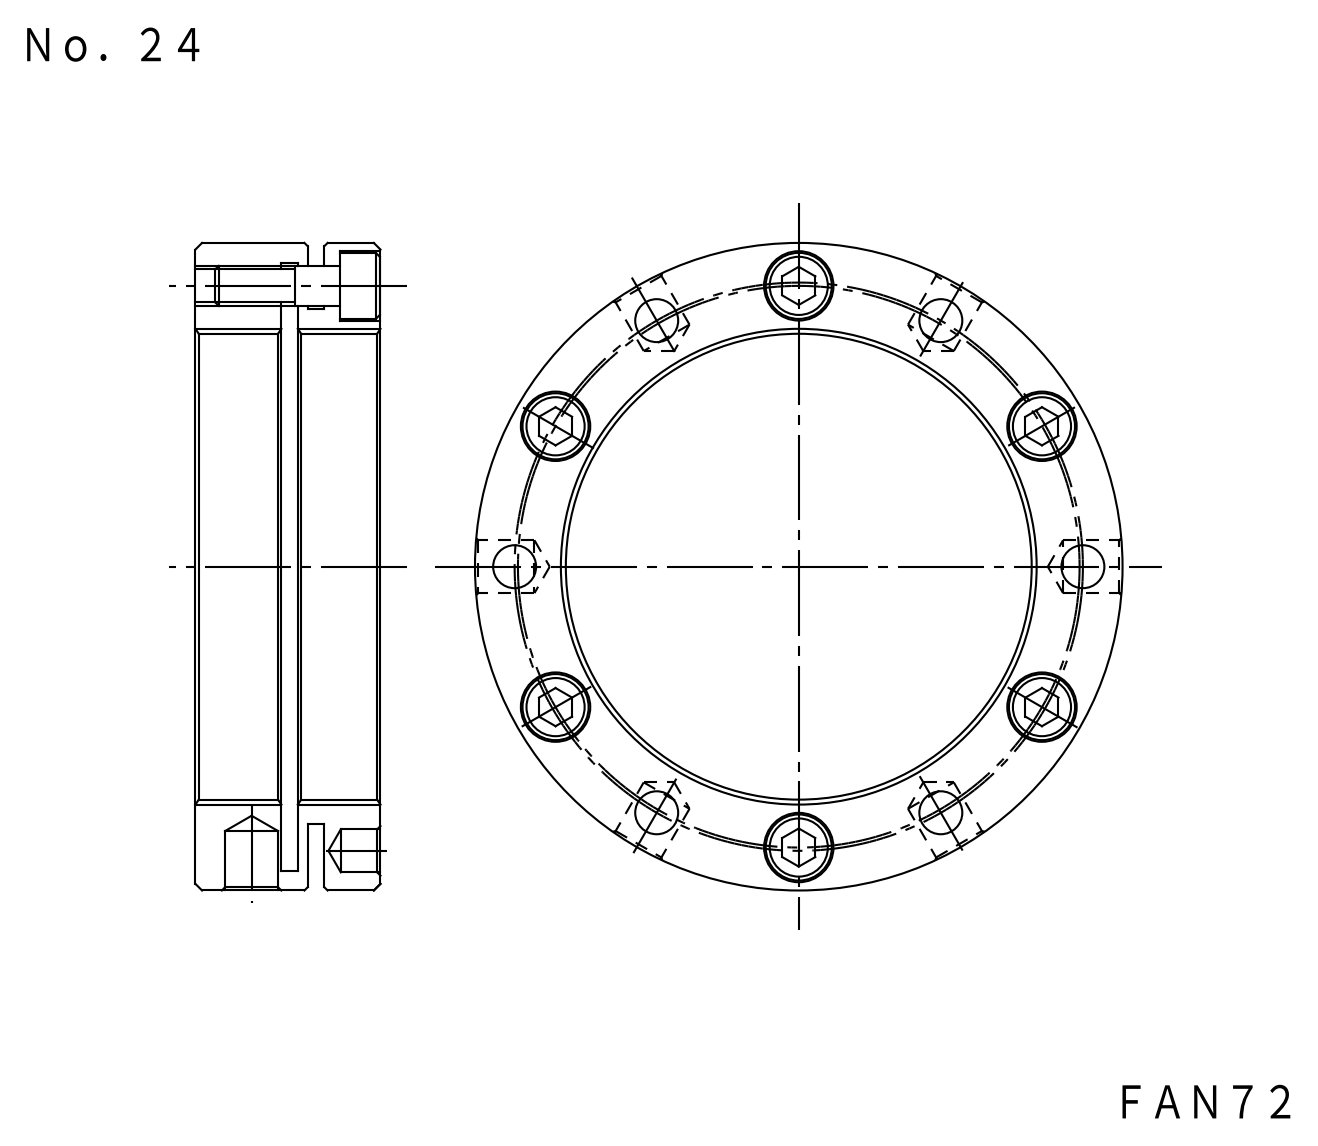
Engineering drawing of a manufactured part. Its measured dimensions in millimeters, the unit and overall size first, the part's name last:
Units: millimetres
Overall size (bounding box): 98 × 98 × 28
Round holes (diameter × count): ⌀6.3 ×6, ⌀6.5 ×6, ⌀10.5 ×6, ⌀4.92 ×3, ⌀4.92 ×3, ⌀8 ×3, ⌀72 ×1, ⌀92 ×1
Round bosses / shafts (diameter × count): ⌀10 ×6, ⌀6 ×6, ⌀98 ×1, ⌀78 ×1
Main face-to-face distances: 2.5, 4, 28, 20, 8, 17.5, 10.5, 13.5, 6.5, 14.5
Hole centre spacings: 42.5, 43, 60.46, 82.59, 22.13, 74.48, 22.14, 73.61
Volume: 80 507 mm³ · Surface area: 41 005 mm²
Bodies: 7 solids, 204 faces (72 planar, 108 cylindrical, 24 other)
Part name (STEP PRODUCT): FKD FAN72; M6X20_default
STEP written by: SolidWorks 2012 (CONFIG_CONTROL_DESIGN)
